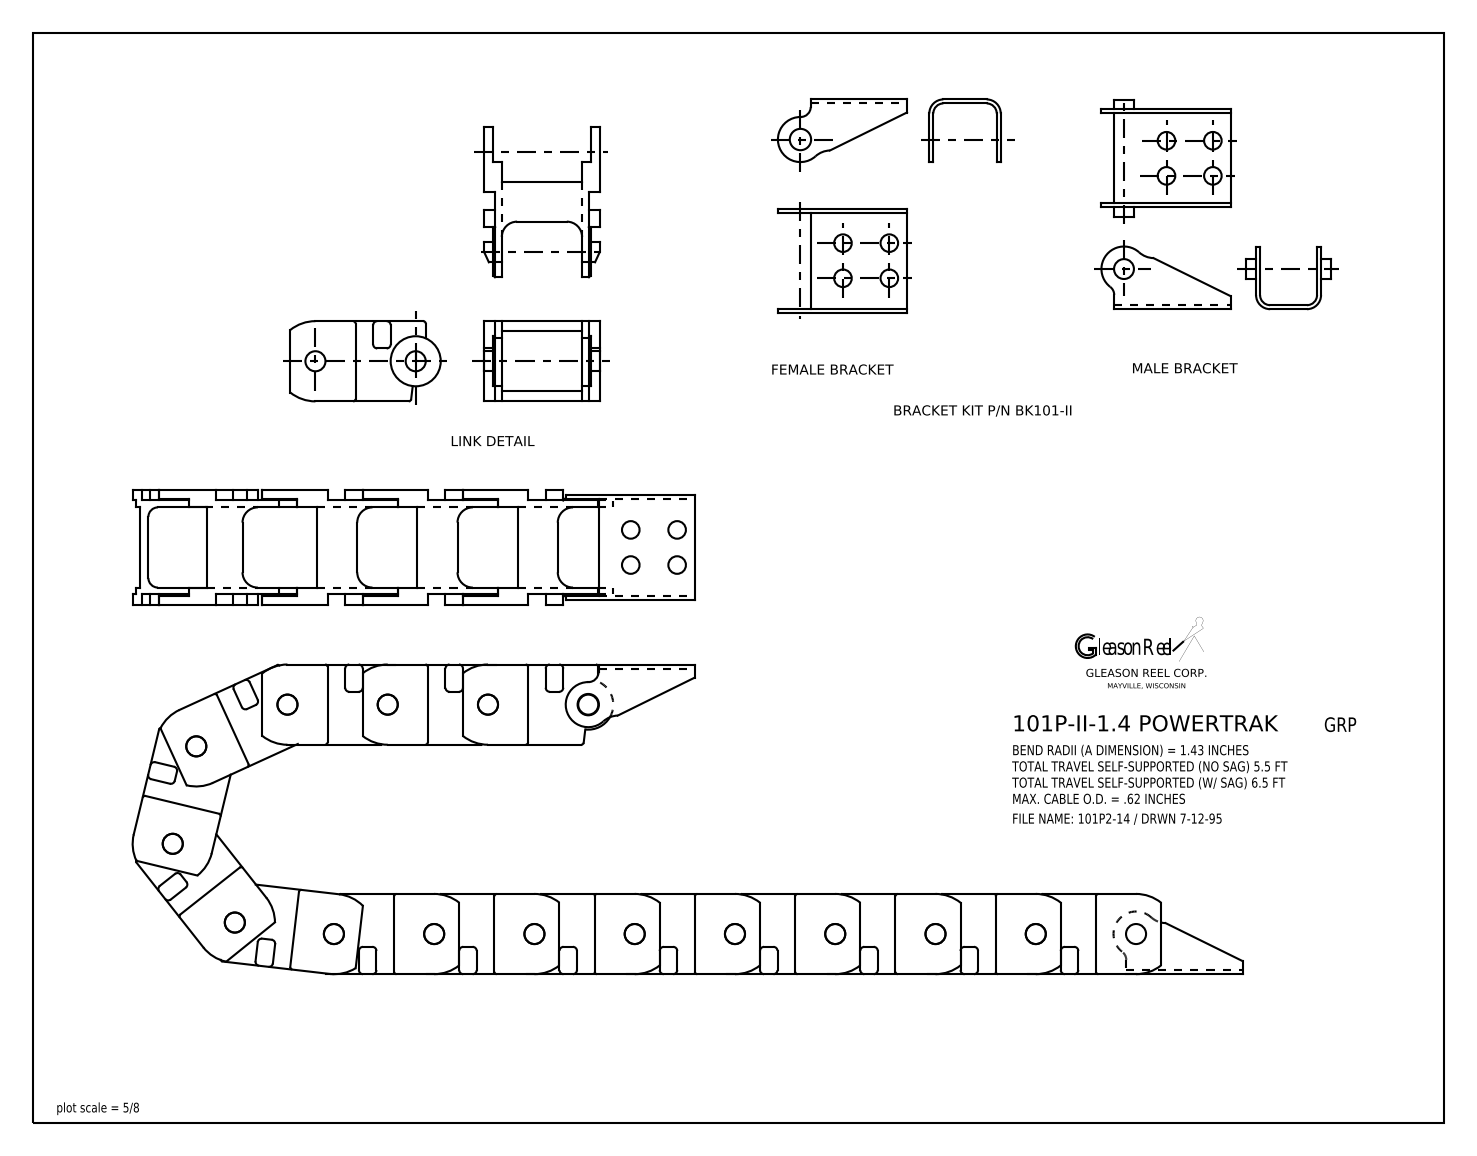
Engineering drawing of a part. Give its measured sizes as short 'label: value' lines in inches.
name: 101P2-14
written by: Autodesk Inventor 2013 (AUTOMOTIVE_DESIGN)
unit: in
bodies: 17 solids, 3922 faces (784 planar, 1806 cylindrical, 1332 other)
size: 13.844 × 3.864 × 1.44
volume: 8.202 in³; area: 175.8 in²
holes: 15× ⌀0.25, 8× ⌀0.219, 1× ⌀0.07, 1× ⌀0.266
bosses: 8× ⌀0.25, 1× ⌀0.2
rounds: 546× R0.01, 289× R0.03, 60× R0.035, 60× R0.05, 60× R0.09, 30× R0.015, 30× R0.19, 15× R0.312
face distances: 1.22, 0.22, 1, 0.11, 0.024, 0.11, 1.196, 1.44, 0.125, 0.875
hole spacings: 1.25, 2.5, 3.75, 0.578, 0.725, 3.398, 4.207, 5
